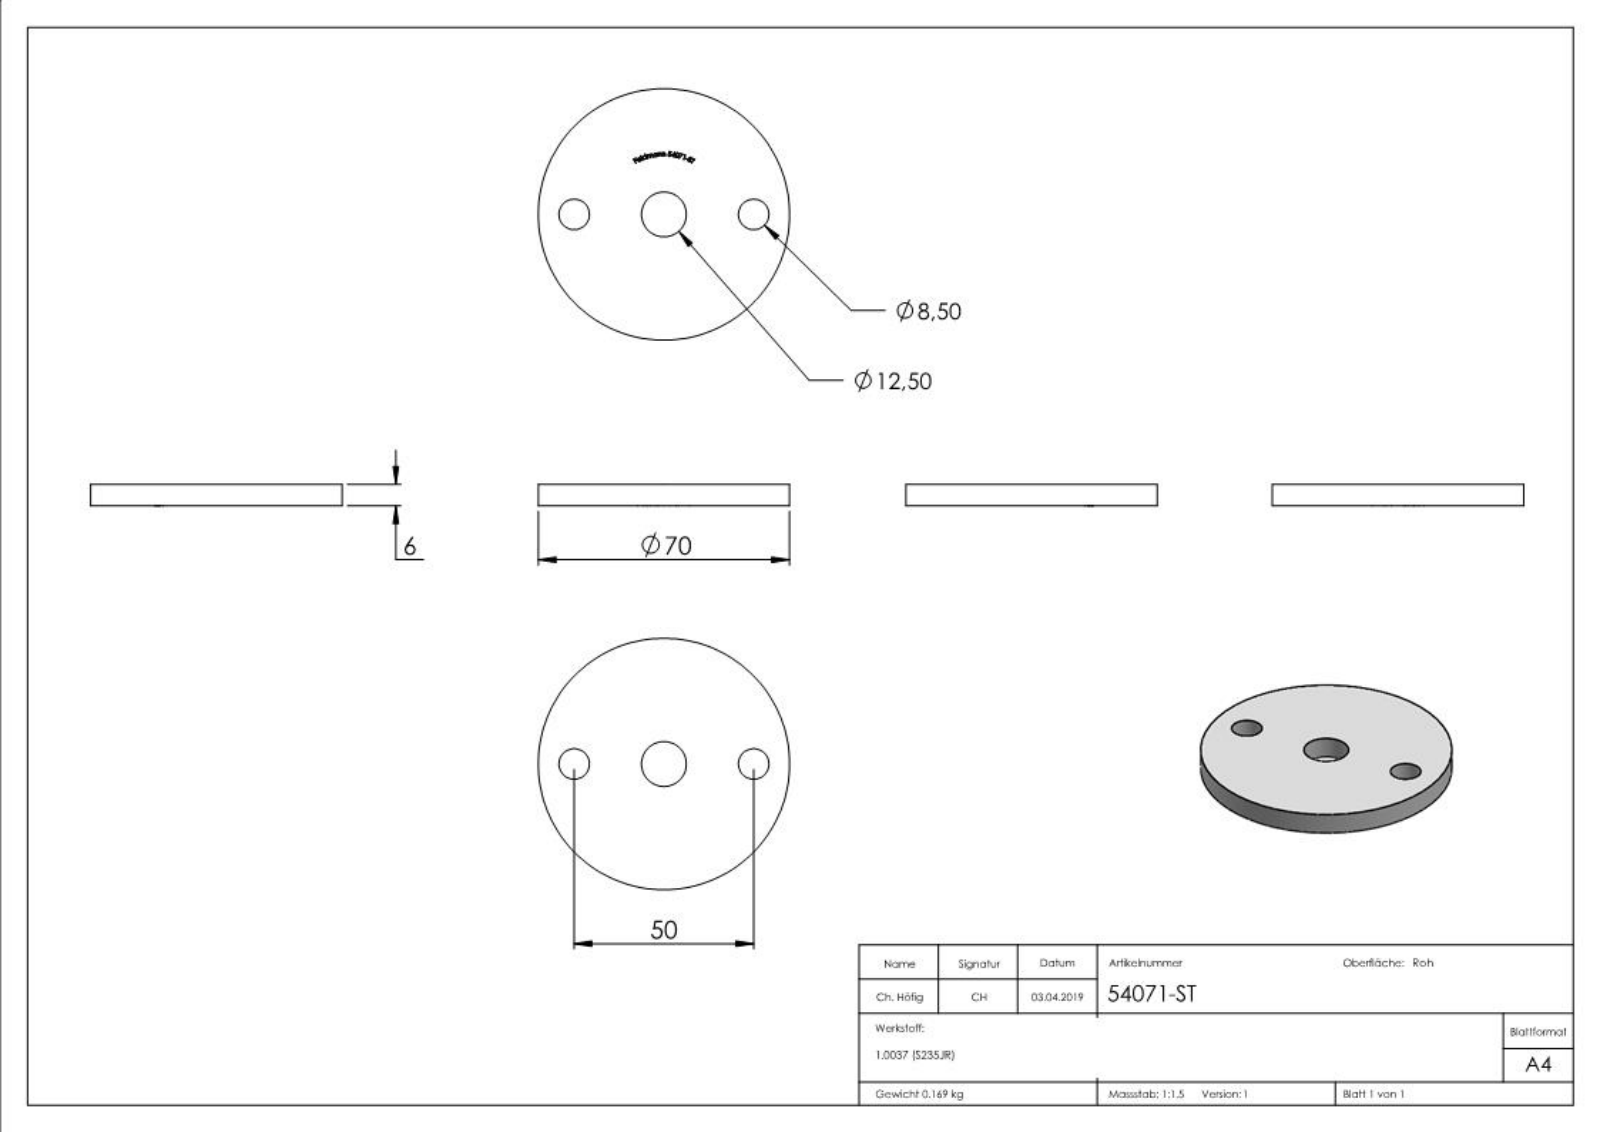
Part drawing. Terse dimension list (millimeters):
name: 54071-ST
written by: SolidWorks 2015 (CONFIG_CONTROL_DESIGN)
unit: mm
bodies: 1 solid, 210 faces (122 planar, 8 cylindrical, 80 other)
size: 70 × 70 × 6
volume: 21 673 mm³; area: 9 108 mm²
holes: 2× ⌀8.5, 1× ⌀12.5
bosses: 1× ⌀70
face distances: 6, 5.9, 0.54, 0.66, 0.67, 0.85, 0.72, 0.79, 1.32, 0.73
hole spacings: 25, 50
